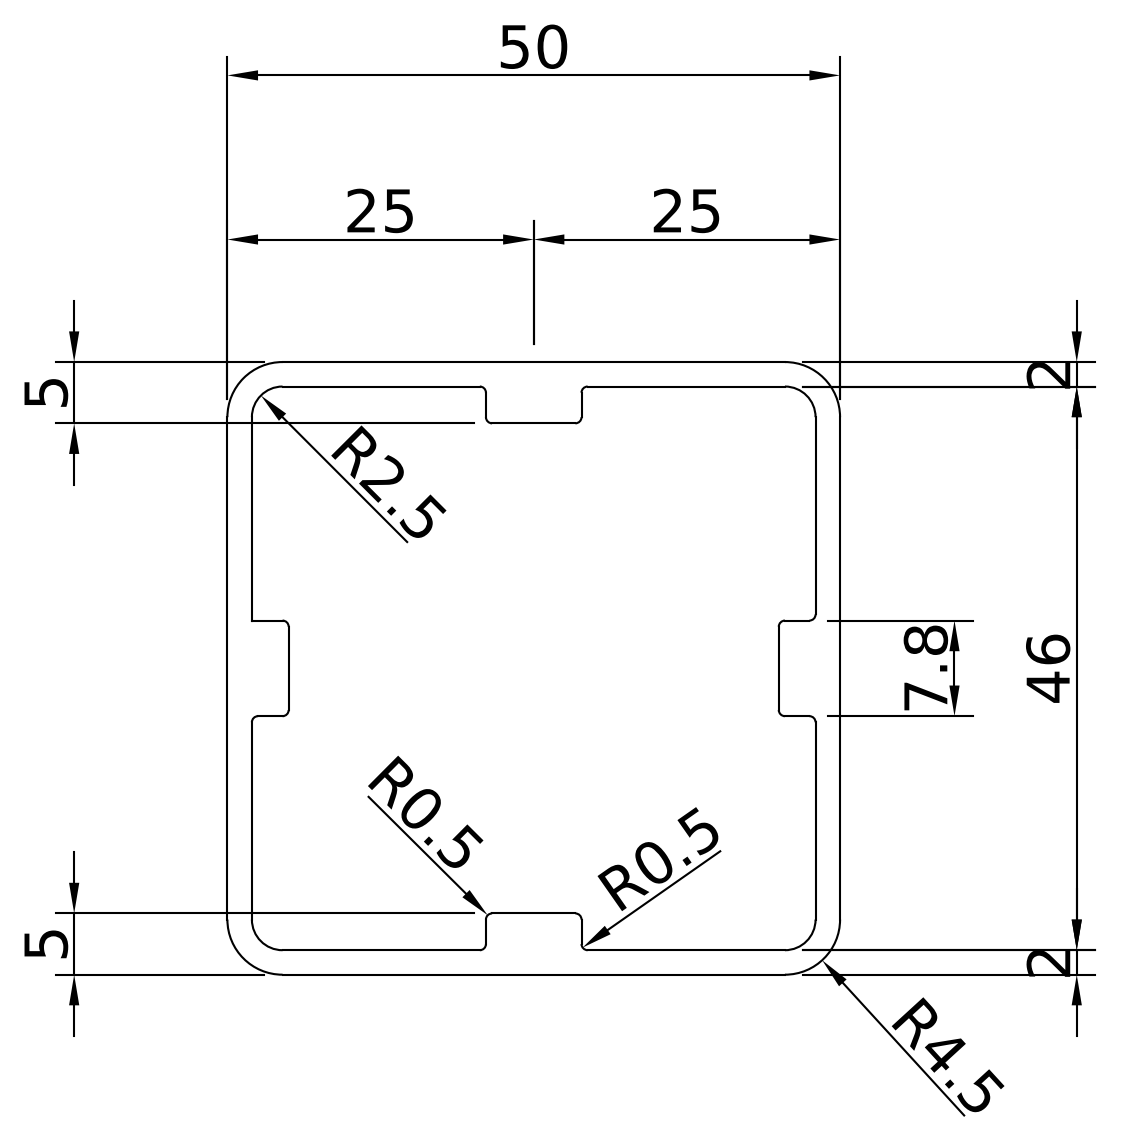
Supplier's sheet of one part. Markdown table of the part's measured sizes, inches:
| quantity | value |
| --- | --- |
| part name | BPRQQ0000026 |
| STEP written by | Autodesk Inventor 2019 (AUTOMOTIVE_DESIGN) |
| units | inches |
| bodies | 1 solid, 49 faces (26 planar, 23 cylindrical, 0 other) |
| overall size | 3.937 × 1.969 × 1.969 |
| volume | 2.841 in³ |
| surface area | 62.32 in² |
| partial cylindrical surfaces (radius × count) | 0.02 × 15, 0.098 × 4, 0.177 × 4 |
| main face-to-face distances | 0.079, 1.89, 1.969, 1.811, 0.197, 1.772, 0.118, 1.693, 0.831, 1.138 |
